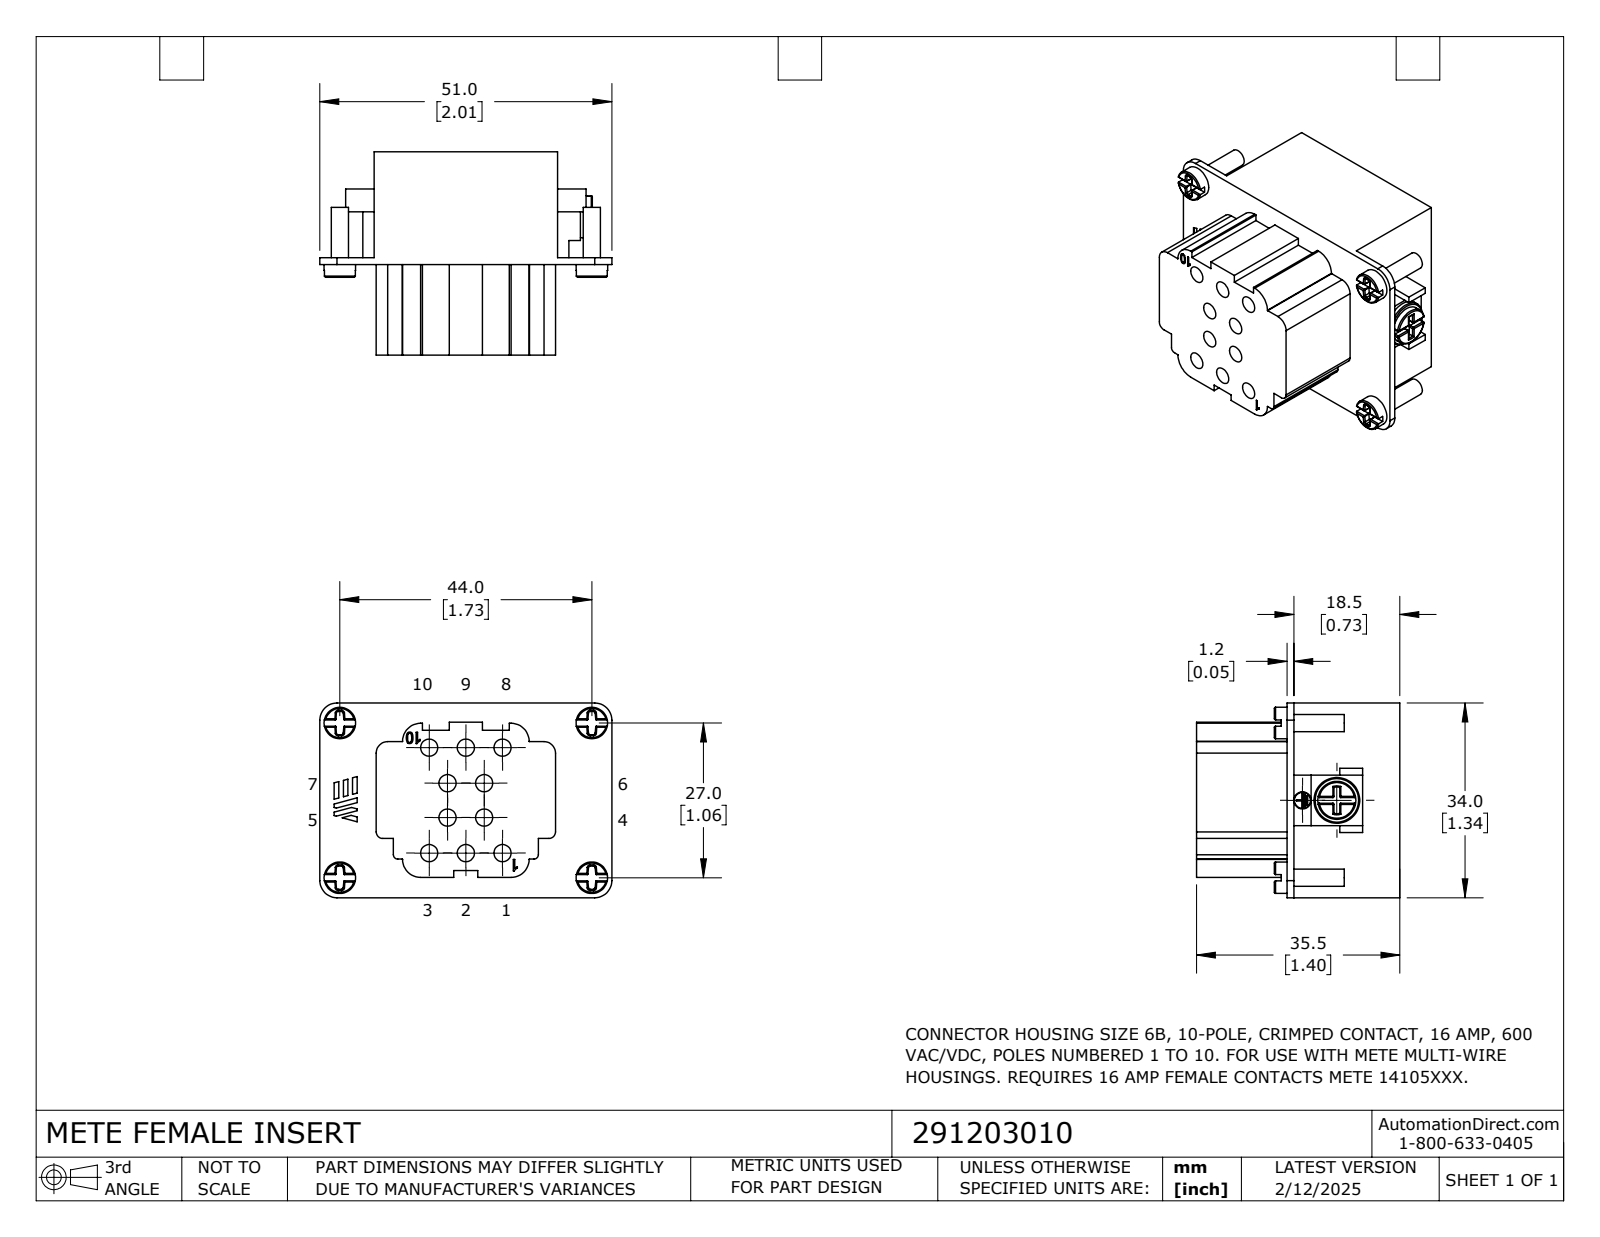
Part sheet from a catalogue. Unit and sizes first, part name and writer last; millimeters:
Units: millimetres
Overall size (bounding box): 51 × 35.5 × 34
Round holes (diameter × count): ⌀3 ×11, ⌀4 ×1
Round bosses / shafts (diameter × count): ⌀5.5 ×4, ⌀3 ×4, ⌀8 ×1, ⌀6.6 ×1, ⌀2.8 ×1
Partial cylindrical surfaces — rounded edges, fillets, slot ends (radius × count): R0.2 ×36, R3 ×4, R3.1 ×4, R0.8 ×2, R1.1 ×2, R2 ×2, R2.3 ×1
Main face-to-face distances: 19.7, 1.2, 34, 15.8, 35.5, 18.5, 17, 32, 0.4, 31.6
Hole centre spacings: 7, 12.6, 6.4, 11.4, 15.5, 19.5, 6, 18.4
Volume: 32 450 mm³ · Surface area: 12 040 mm²
Bodies: 1 solid, 417 faces (199 planar, 124 cylindrical, 94 other)
Part name (STEP PRODUCT): 291203010
STEP written by: SolidWorks 2024 (CONFIG_CONTROL_DESIGN)
